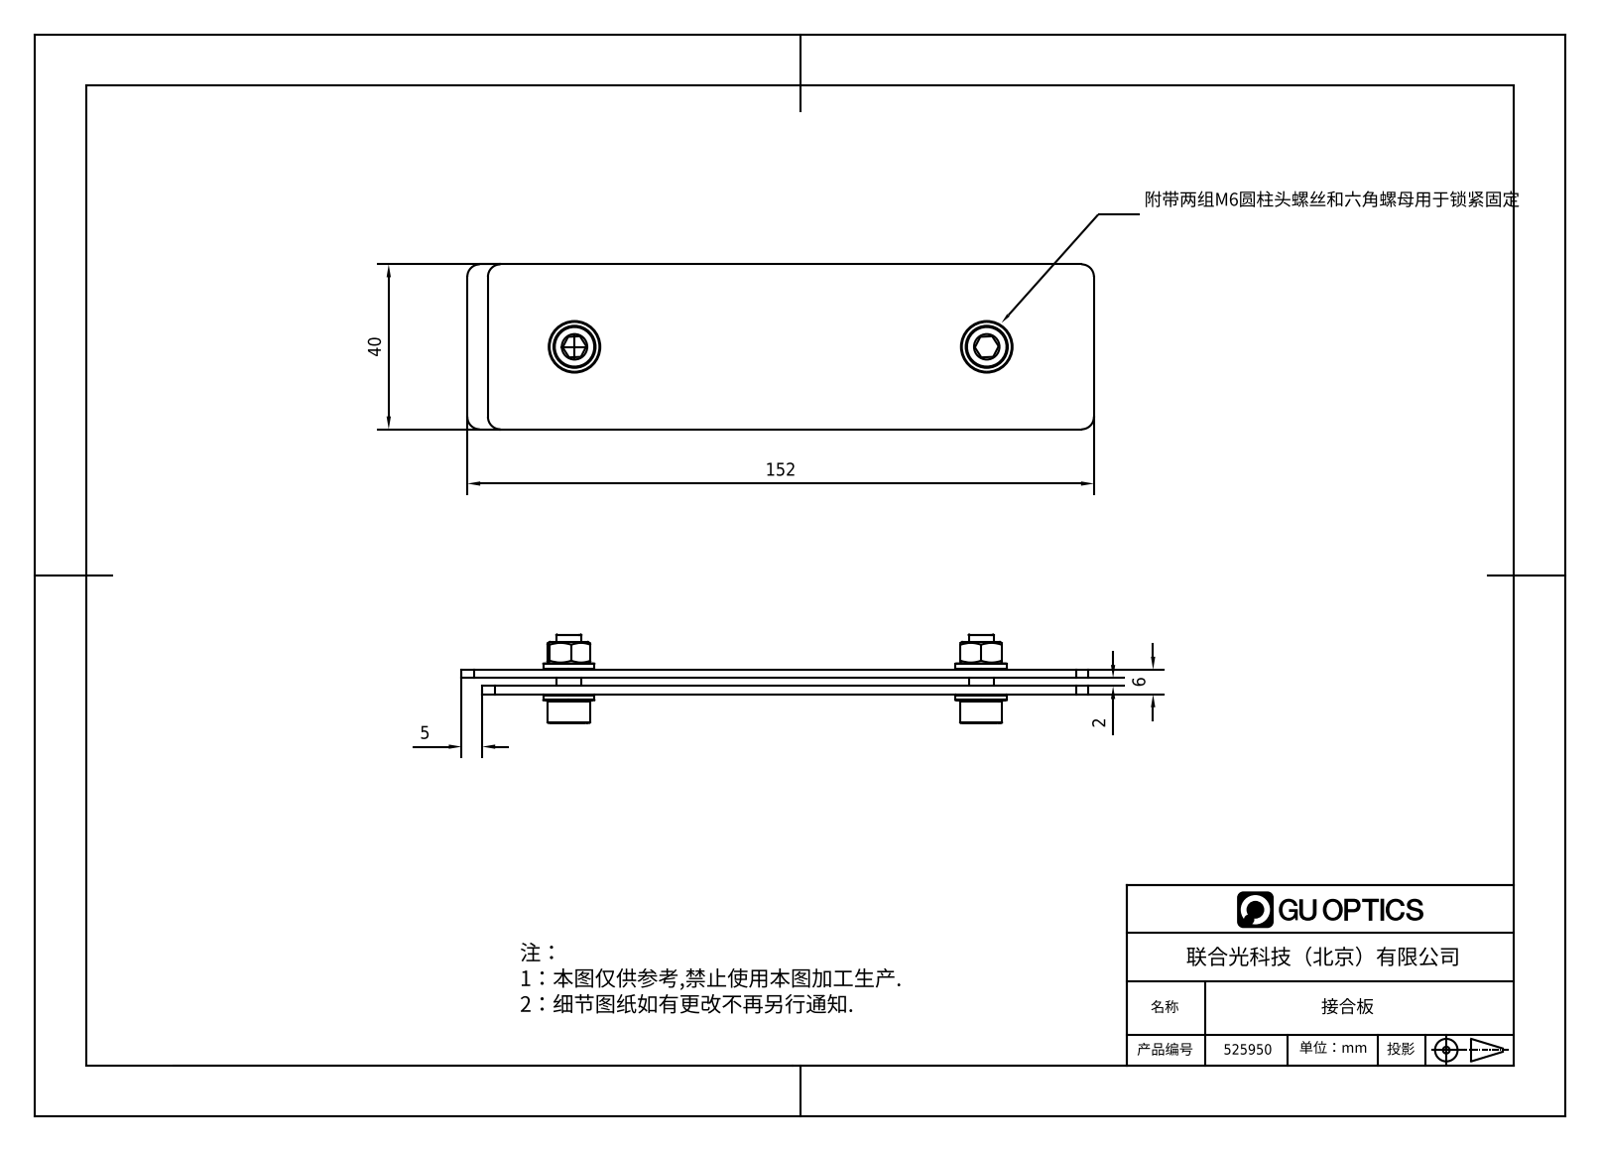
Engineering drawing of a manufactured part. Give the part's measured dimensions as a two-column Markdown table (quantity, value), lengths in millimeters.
| quantity | value |
| --- | --- |
| part name | 525950 |
| STEP written by | SolidWorks 2020 (CONFIG_CONTROL_DESIGN) |
| units | millimeters |
| bodies | 10 solids, 114 faces (56 planar, 26 cylindrical, 32 other) |
| overall size | 152 × 40 × 21.5 |
| volume | 26 525 mm³ |
| surface area | 28 397 mm² |
| round holes (diameter × count) | 4.92 × 2, 6.4 × 2, 6.6 × 2 |
| round bosses / shafts (diameter × count) | 12.5 × 2, 10.2 × 2, 6 × 2 |
| partial cylindrical surfaces (radius × count) | 3 × 6 |
| main face-to-face distances | 2, 4, 6, 40, 5.5, 1.5, 3.5, 7.5, 9, 10 |
| hole center spacings | 100 |
